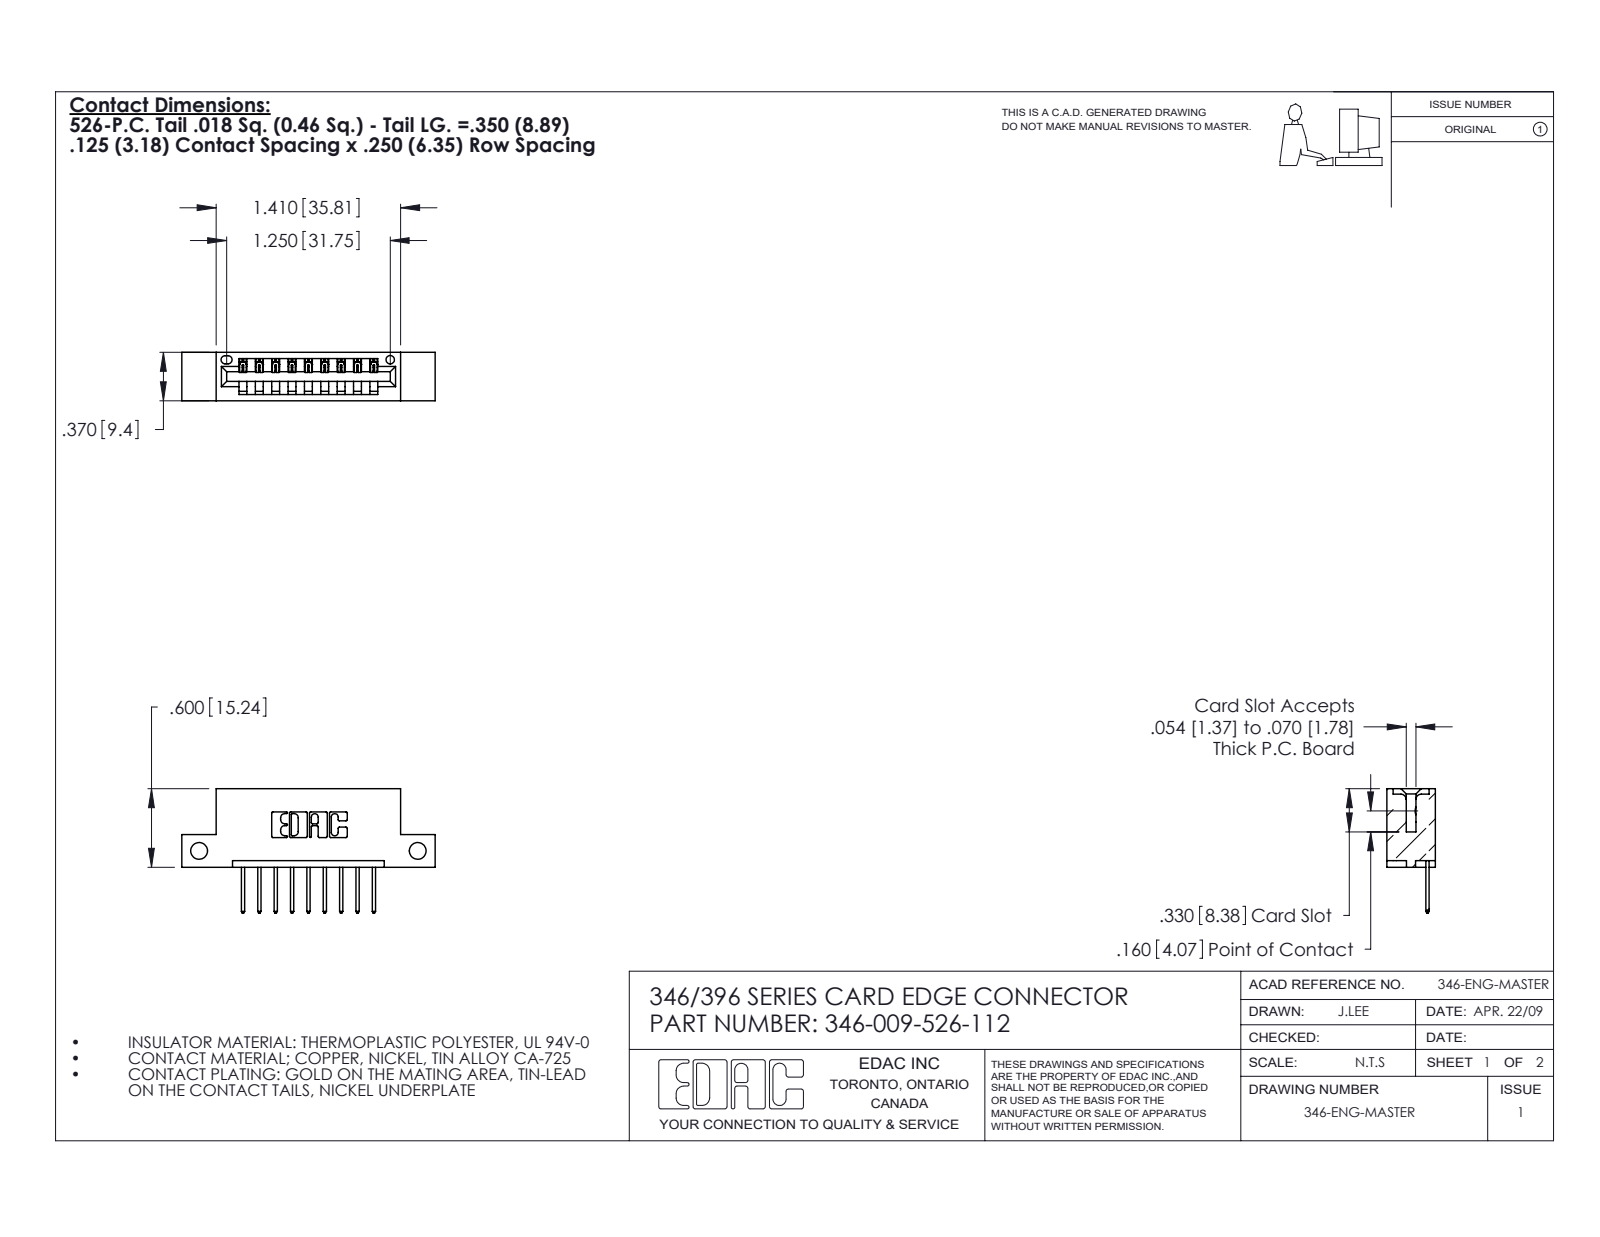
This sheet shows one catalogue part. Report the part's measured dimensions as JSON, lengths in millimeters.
{"part_name": "346 Part_Flush Mounting Lugs - Side Mount; 346-009-526-112; 345-292-001_345-293-126", "step_written_by": "SolidWorks 2020 (CONFIG_CONTROL_DESIGN)", "units": "millimeters", "bodies": {"solids": 10, "faces": 644, "planar": 436, "cylindrical": 208, "other": 0}, "overall_size": [49.1, 24.1, 9.4], "volume_mm3": 4380, "surface_area_mm2": 4967, "round_holes": [[3.3, 2], [1.6, 1]], "partial_cylinders_radius": [[0.3, 22], [0.2, 18], [0.3, 18], [0.2, 6], [0.8, 6], [0.7, 3], [0.8, 2], [1, 2]], "face_to_face_distances": [6.4, 1.2, 8.2, 9.4, 1.8, 7.6, 0.6, 3.8, 5.6, 2.5], "hole_center_spacings": [42.4]}
